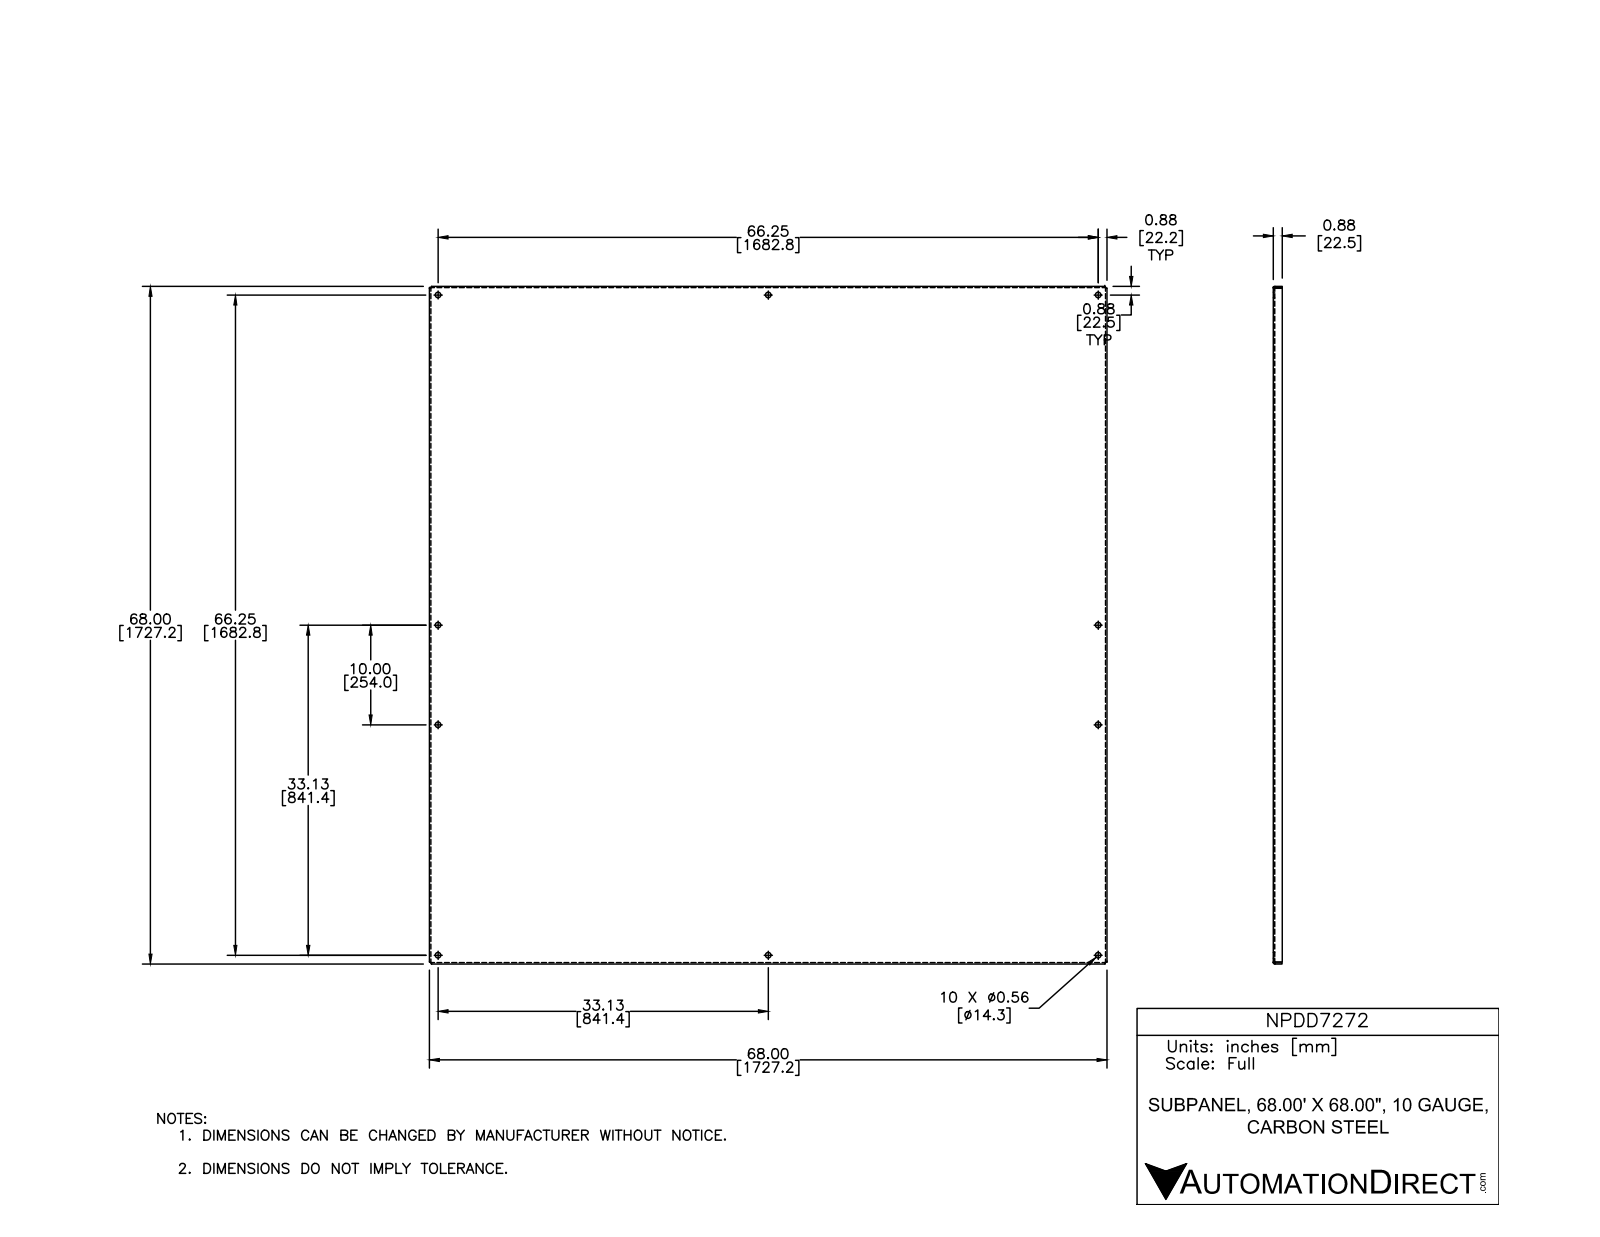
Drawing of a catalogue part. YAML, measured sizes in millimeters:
part_name: "NPDD4242-NPDD7272"
step_written_by: "Autodesk Inventor 2012 (AUTOMOTIVE_DESIGN)"
units: millimeters
bodies: {solids: 1, faces: 48, planar: 22, cylindrical: 18, other: 8}
overall_size: [1727.2, 1727.2, 22.2]
volume: 9858000
surface_area: 6234000
round_holes:
  - {diameter: 14.3, count: 10}
partial_cylinders:
  - {radius: 0.8, count: 4}
  - {radius: 4, count: 4}
face_to_face_distances: [3.2, 1724, 1727.2, 1720.9, 1724, 1720.9, 3.2, 19.1, 22.2, 5.4]
hole_center_spacings: [841.4, 1881.4, 1682.8, 1189.9, 254, 587.4, 841.4, 1095.4]
